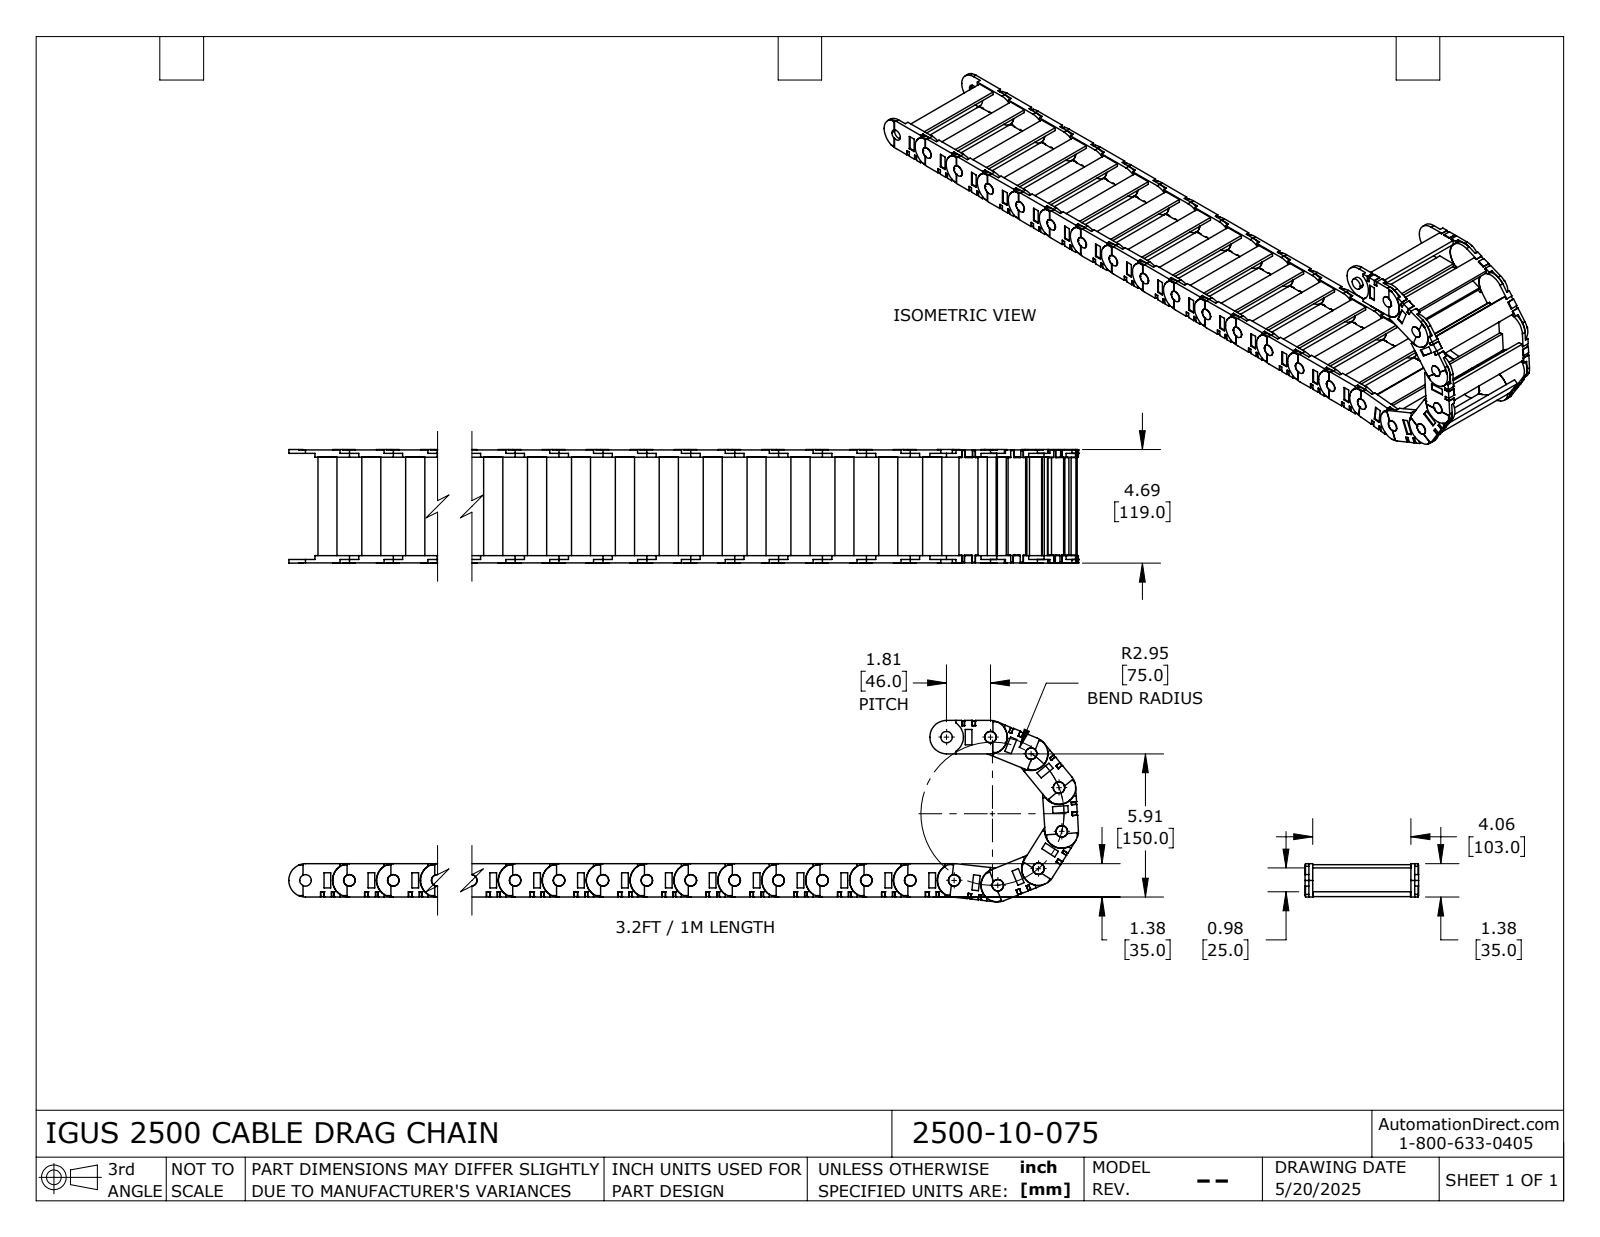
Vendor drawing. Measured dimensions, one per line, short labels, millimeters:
name: 2500_10_075
written by: SolidWorks 2024 (AUTOMOTIVE_DESIGN)
unit: mm
bodies: 66 solids, 2398 faces (1870 planar, 528 cylindrical, 0 other)
size: 837.7 × 190.1 × 119
volume: 910 300 mm³; area: 526 300 mm²
holes: 22× ⌀12
bosses: 22× ⌀12, 21× ⌀35
rounds: 23× R17.7, 2× R17.5
face distances: 4, 107, 111, 25, 3.6, 3.4, 5, 7.6, 110.6, 114.6
hole spacings: 46, 92, 138, 184, 230, 276, 322, 368
